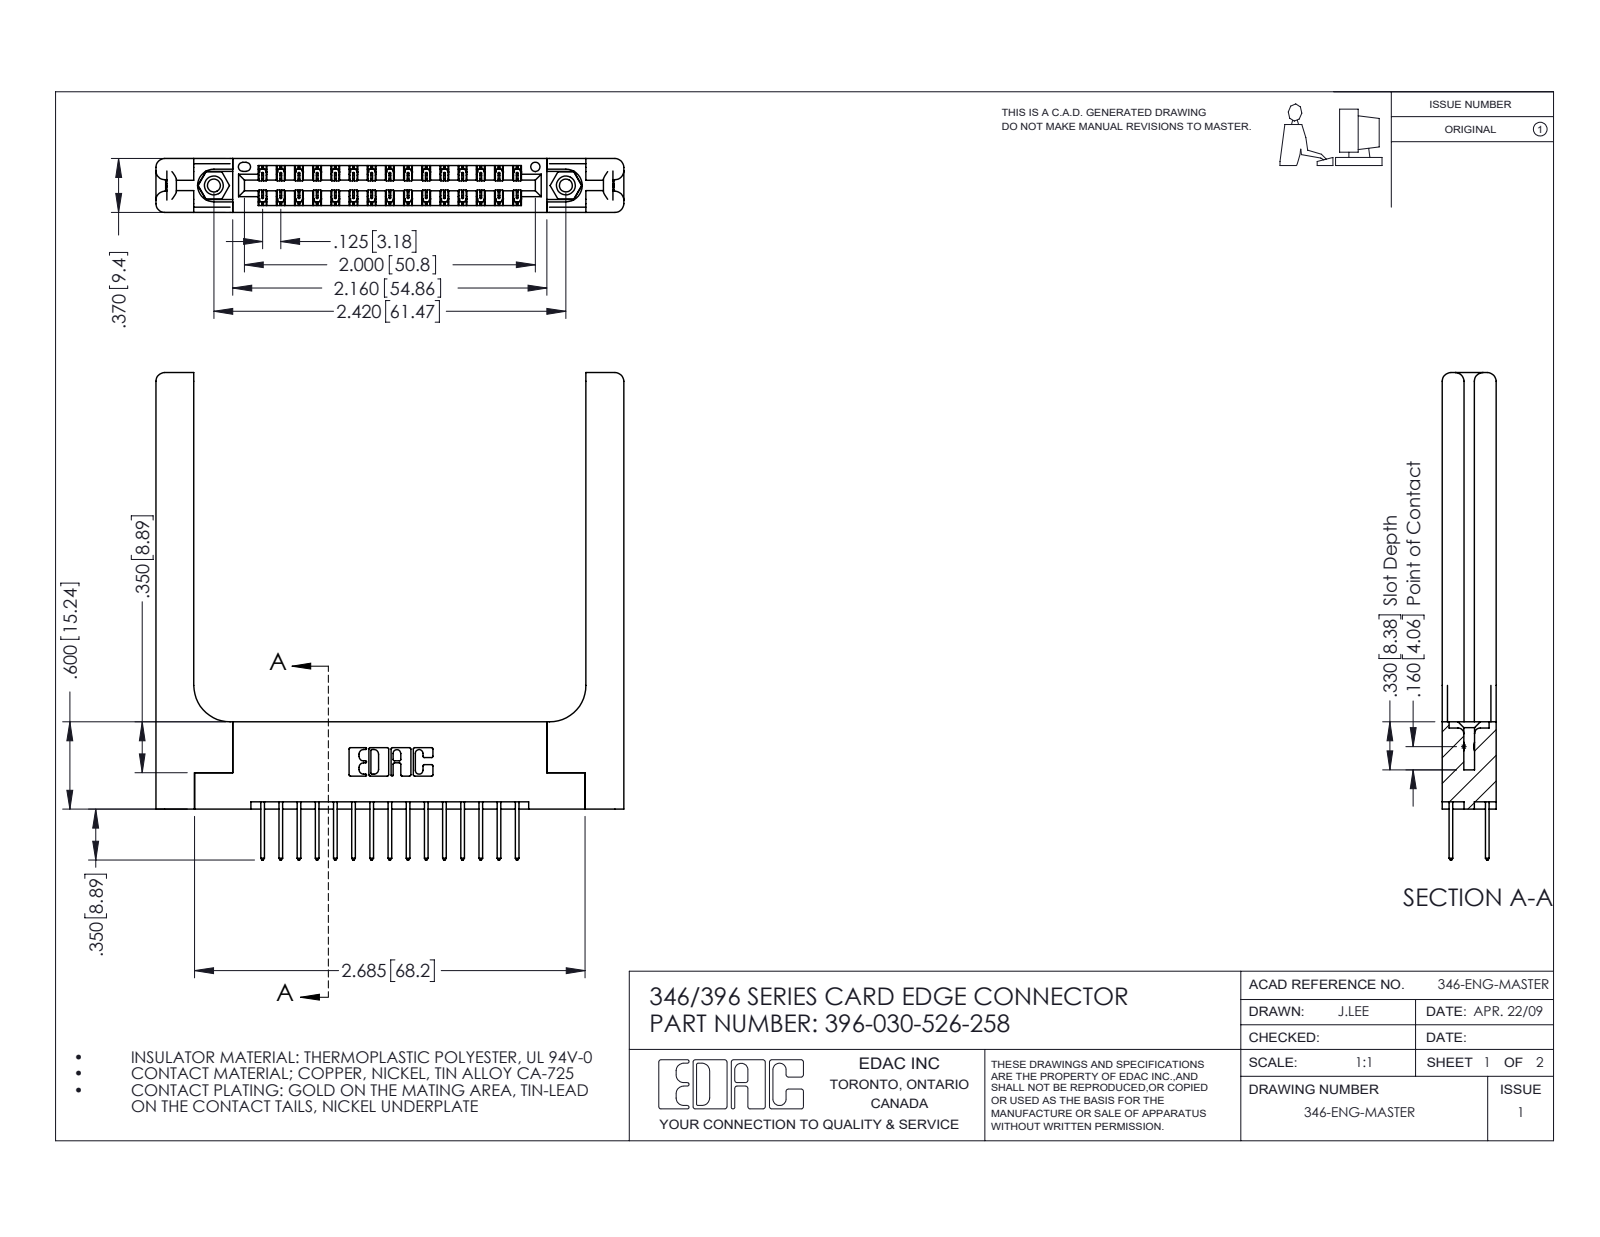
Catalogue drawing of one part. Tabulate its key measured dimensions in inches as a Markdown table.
| quantity | value |
| --- | --- |
| part name | 345-292-001_345-293-126; 396-030-526-258; 346-220-058_345-220-058; 345-250-001_345-250-001-102 (+1 more) |
| STEP written by | SolidWorks 2016 (CONFIG_CONTROL_DESIGN) |
| units | inches |
| bodies | 35 solids, 1938 faces (1274 planar, 604 cylindrical, 60 other) |
| overall size | 3.35 × 3.216 × 0.37 |
| volume | 0.934 in³ |
| surface area | 24.02 in² |
| round holes (diameter × count) | 0.089 × 2, 0.125 × 2, 0.156 × 2, 0.064 × 1 |
| round bosses / shafts (diameter × count) | 0.155 × 2 |
| partial cylindrical surfaces (radius × count) | 0.006 × 45, 0.01 × 30, 0.01 × 22, 0.06 × 16, 0.007 × 6, 0.031 × 6, 0.026 × 3, 0.014 × 2 |
| main face-to-face distances | 0.37, 0.072, 0.148, 0.15, 0.048, 0.322, 0.25, 0.077, 0.025, 0.298 |
| hole center spacings | 0.246, 2.213, 2.42 |
